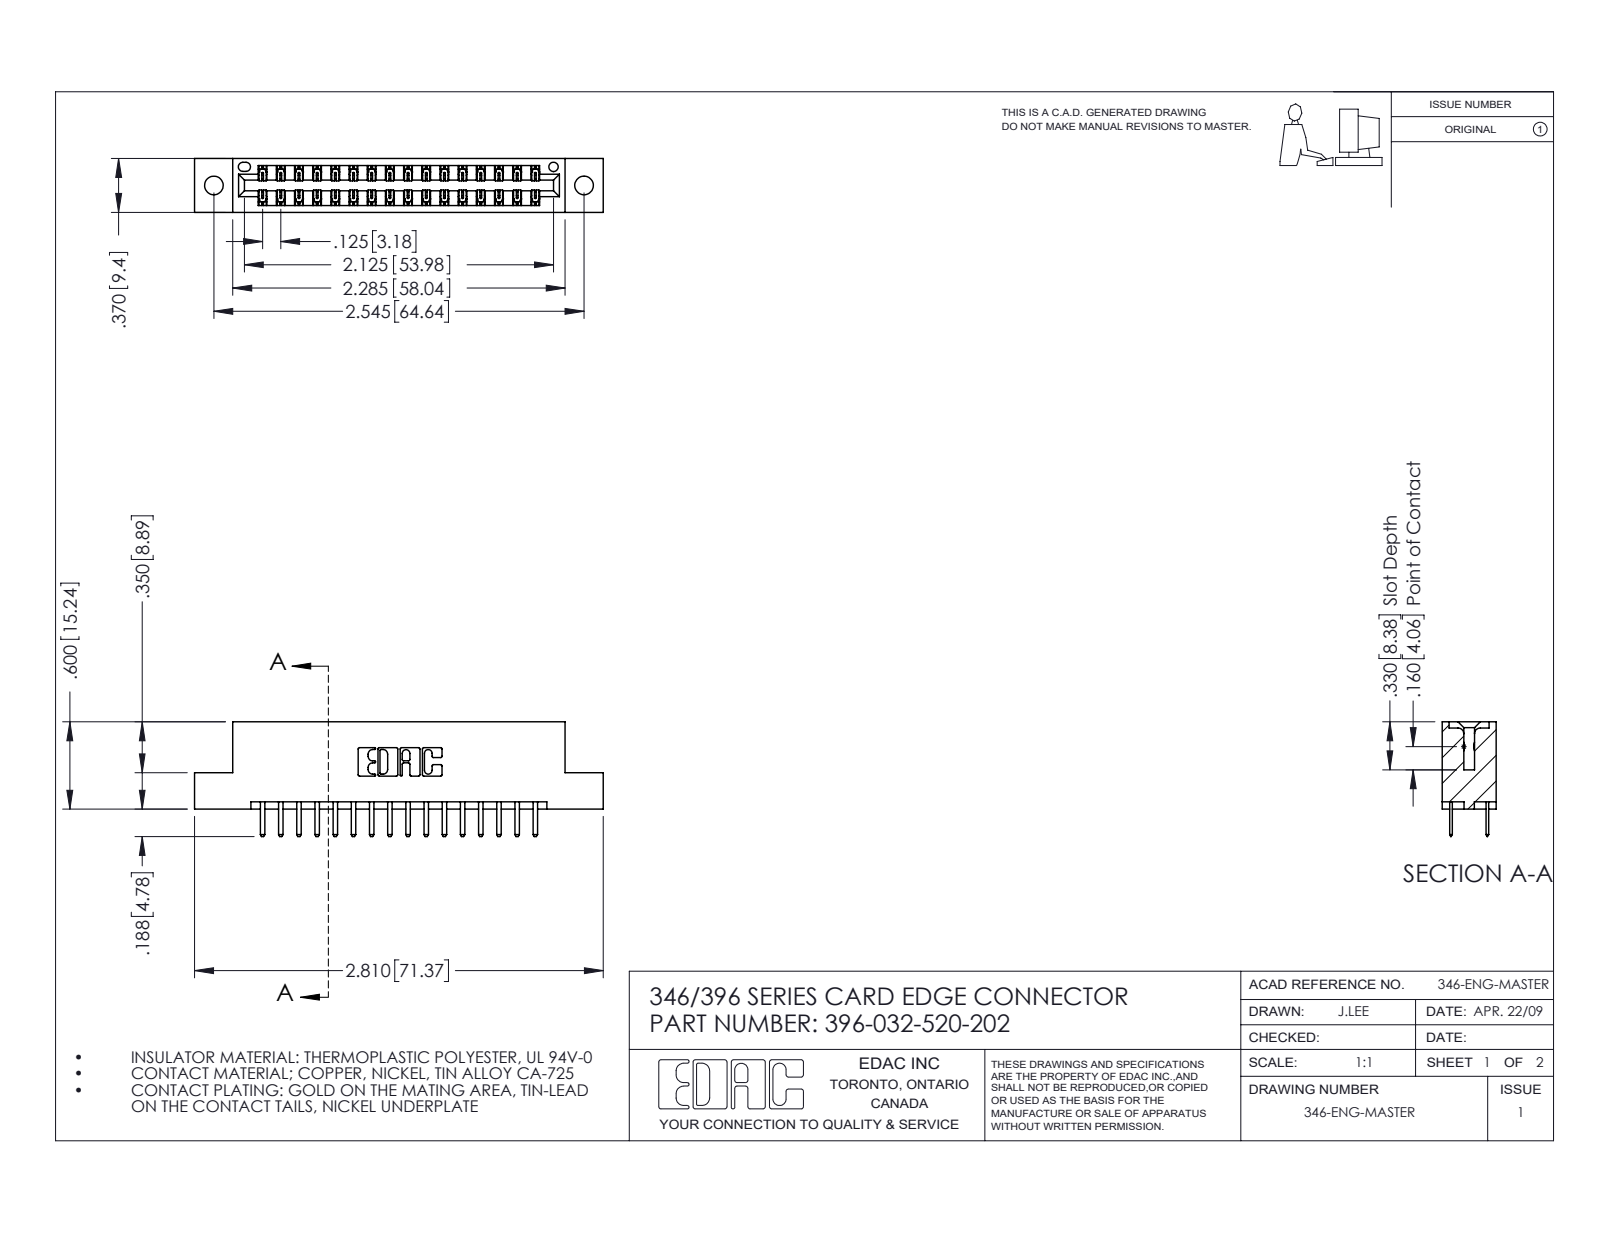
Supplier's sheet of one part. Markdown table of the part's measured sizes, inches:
| quantity | value |
| --- | --- |
| part name | 396-032-520-202; 346 Part_Flush Mounting Lugs - 0.128 Dia; 345-292-001_345-293-120 |
| STEP written by | SolidWorks 2016 (CONFIG_CONTROL_DESIGN) |
| units | inches |
| bodies | 33 solids, 1914 faces (1260 planar, 654 cylindrical, 0 other) |
| overall size | 2.81 × 0.788 × 0.37 |
| volume | 0.409 in³ |
| surface area | 13.19 in² |
| round holes (diameter × count) | 0.128 × 2, 0.064 × 1 |
| partial cylindrical surfaces (radius × count) | 0.006 × 48, 0.01 × 36, 0.01 × 22, 0.007 × 6, 0.031 × 6, 0.026 × 3, 0.014 × 2, 0.022 × 2 |
| main face-to-face distances | 0.25, 0.048, 0.322, 0.37, 0.275, 0.072, 0.298, 0.025, 0.148, 0.222 |
| hole center spacings | 0.246, 2.338, 2.545 |
